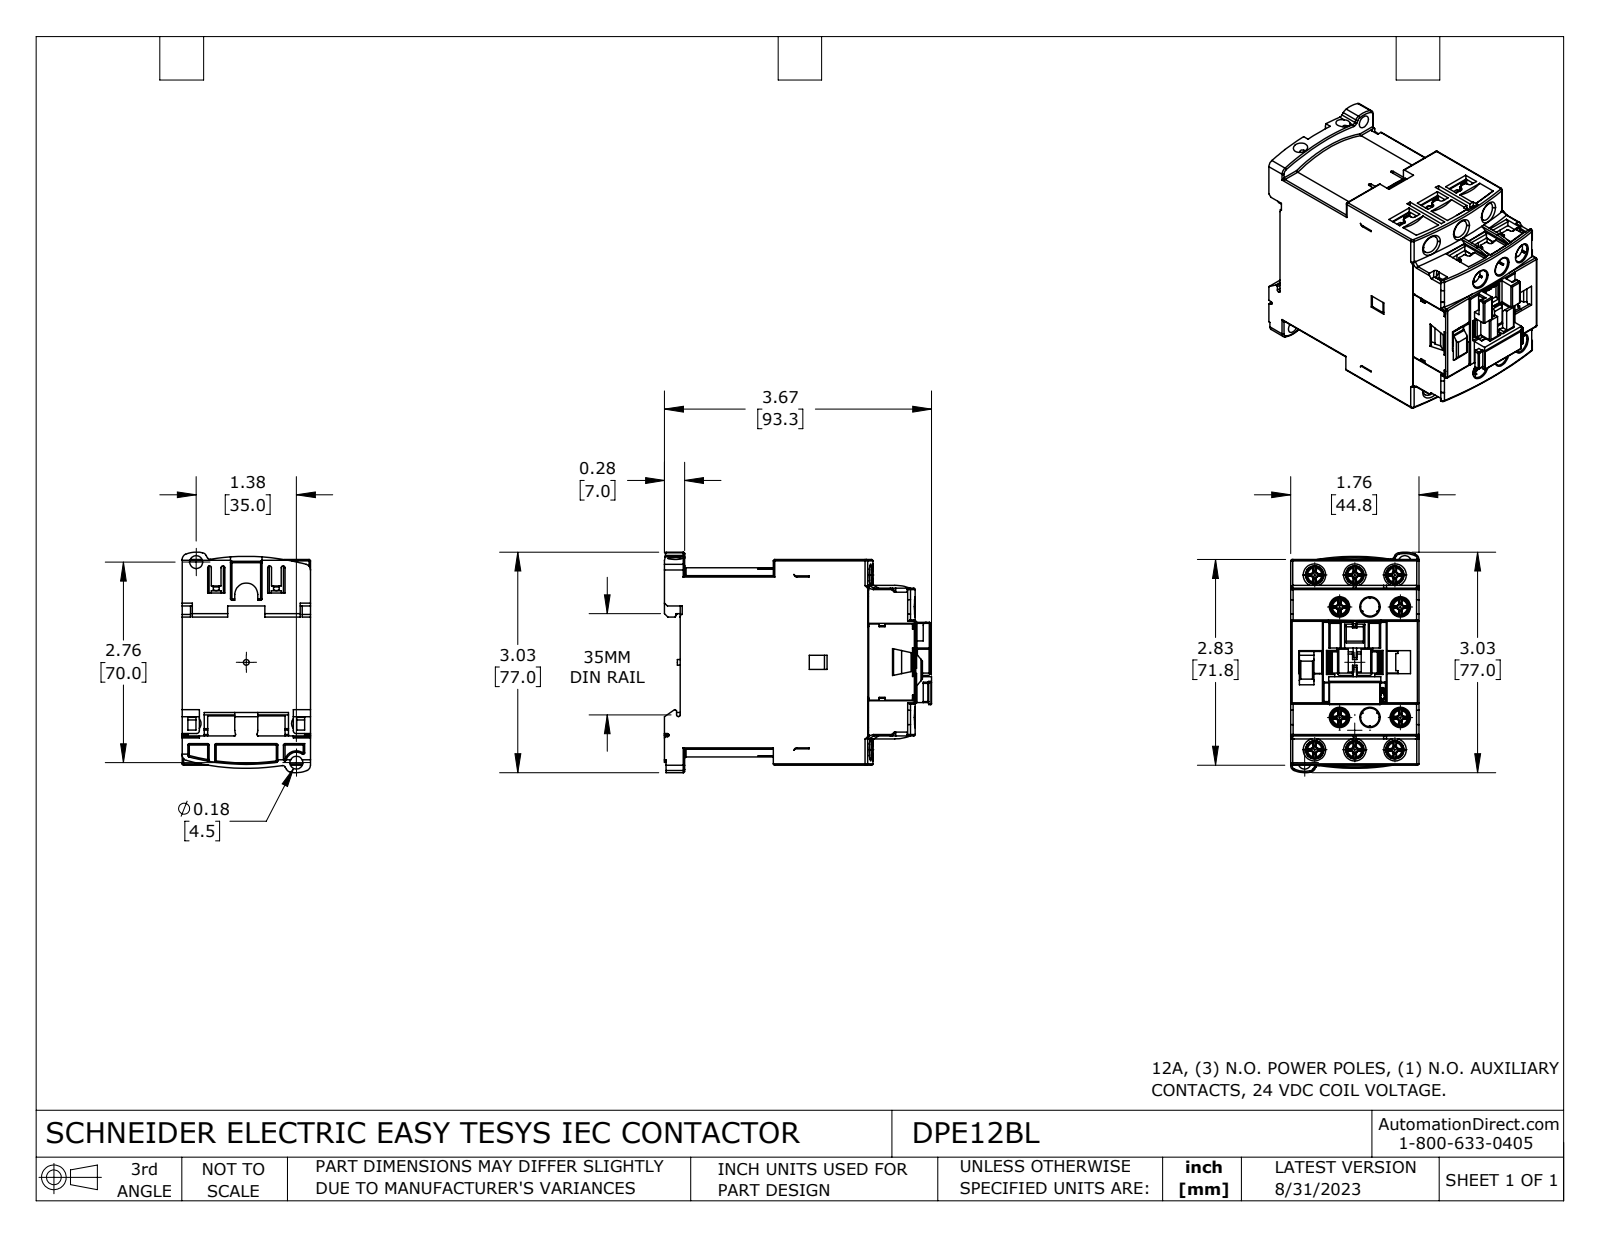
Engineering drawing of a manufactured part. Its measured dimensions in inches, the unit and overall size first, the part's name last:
Units: inches
Overall size (bounding box): 3.671 × 3.031 × 1.764
Round holes (diameter × count): ⌀0.252 ×6, ⌀0.256 ×6, ⌀0.039 ×2, ⌀0.177 ×2, ⌀0.197 ×2, ⌀0.098 ×1, ⌀0.167 ×1, ⌀0.236 ×1
Round bosses / shafts (diameter × count): ⌀0.138 ×10, ⌀0.108 ×10, ⌀0.315 ×6, ⌀0.157 ×2, ⌀0.079 ×1
Partial cylindrical surfaces — rounded edges, fillets, slot ends (radius × count): R0.02 ×91, R0.006 ×42, R0.039 ×34, R0.012 ×31, R0.016 ×22, R0.008 ×14, R0.031 ×10, R0.157 ×9
Main face-to-face distances: 1.764, 0.272, 2.579, 2.555, 0.047, 0.217, 0.15, 2.283, 1.717, 0.173
Hole centre spacings: 0.417, 0.551, 1.576, 2.464, 1.52, 2.402, 0.224, 0.274
Volume: 12.53 in³ · Surface area: 94.96 in²
Bodies: 10 solids, 3575 faces (2470 planar, 705 cylindrical, 400 other)
Part name (STEP PRODUCT): DPE12BL
STEP written by: SolidWorks 2021 (CONFIG_CONTROL_DESIGN)
